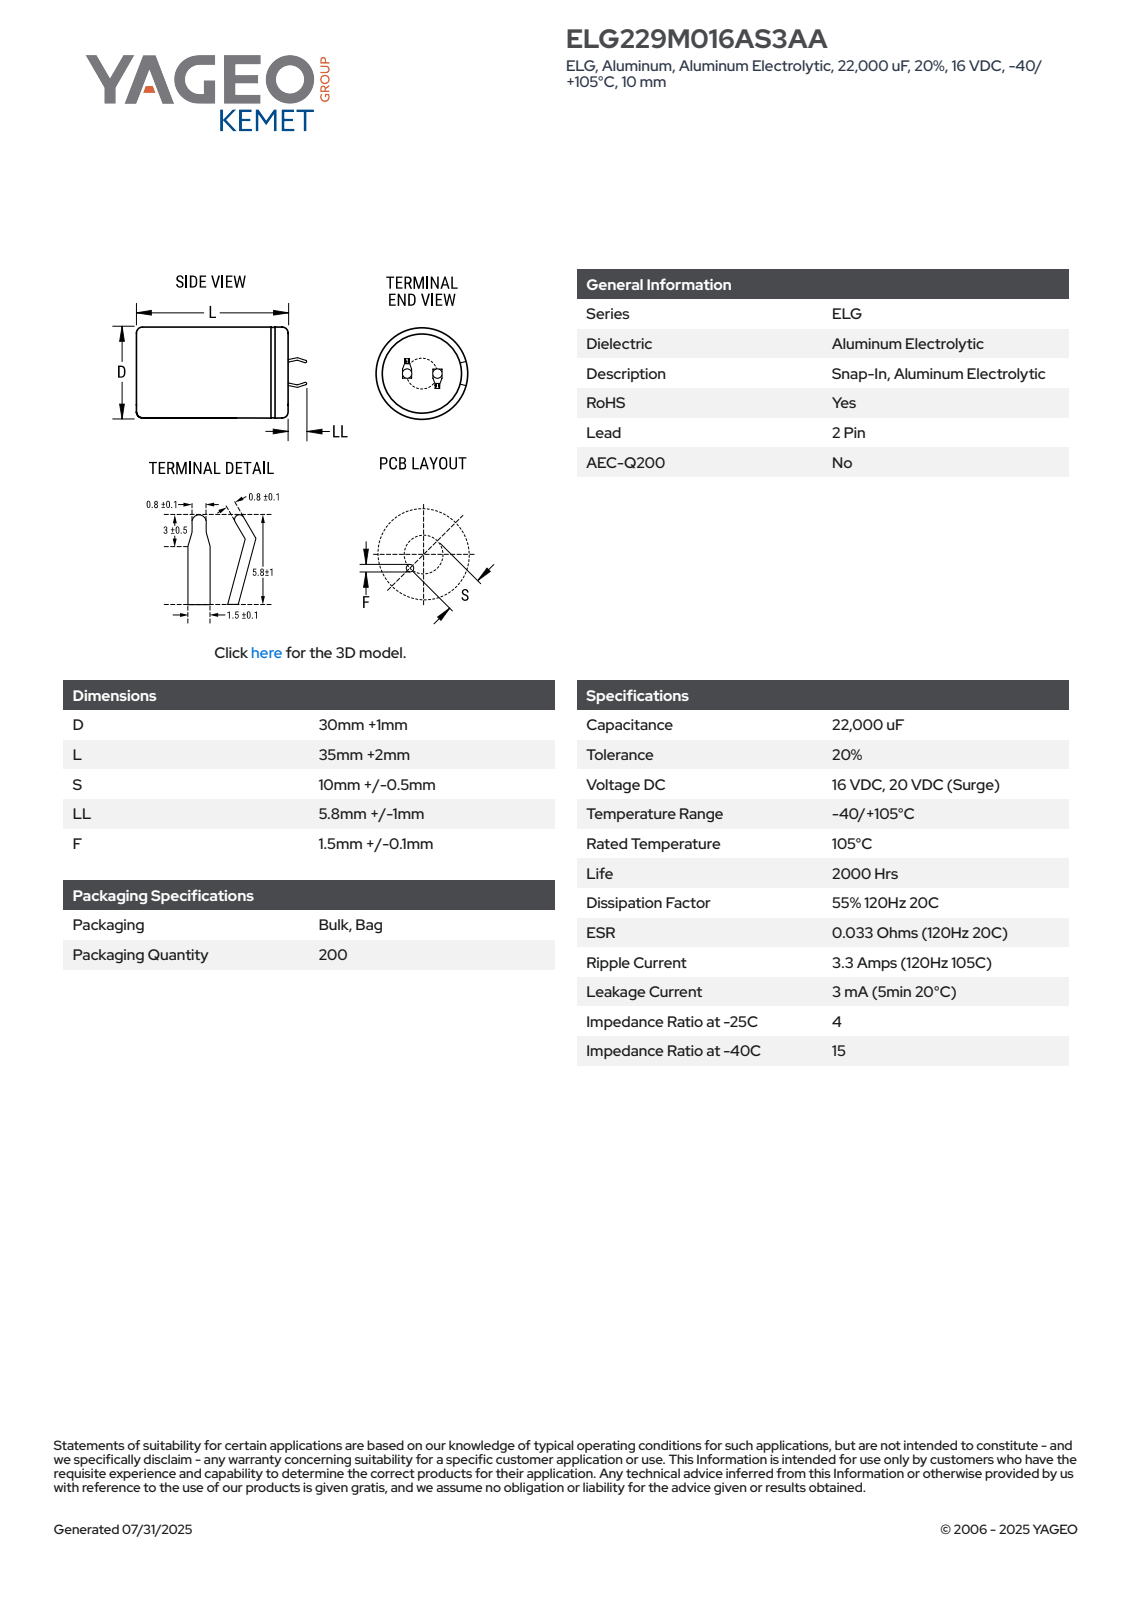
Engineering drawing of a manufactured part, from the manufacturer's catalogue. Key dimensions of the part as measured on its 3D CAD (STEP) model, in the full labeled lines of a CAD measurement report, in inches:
Part name (STEP PRODUCT): CARS_K2P_30X35_D31L37S10LL6.8F1.6
STEP written by: SolidWorks 2014 (AUTOMOTIVE_DESIGN)
Units: inches
Bodies: 1 solid, 100 faces (52 planar, 9 cylindrical, 39 other)
Overall size (bounding box): 1.724 × 1.22 × 1.22
Volume: 1.684 in³ · Surface area: 7.938 in²
Round holes (diameter × count): ⌀1.08 ×1
Round bosses / shafts (diameter × count): ⌀1.22 ×1
Partial cylindrical surfaces — rounded edges, fillets, slot ends (radius × count): R0.61 ×1
Main face-to-face distances: 1.456, 1.476, 0.02, 0.024, 0.279, 0.03, 0.053, 0.302, 0.255, 0.023
